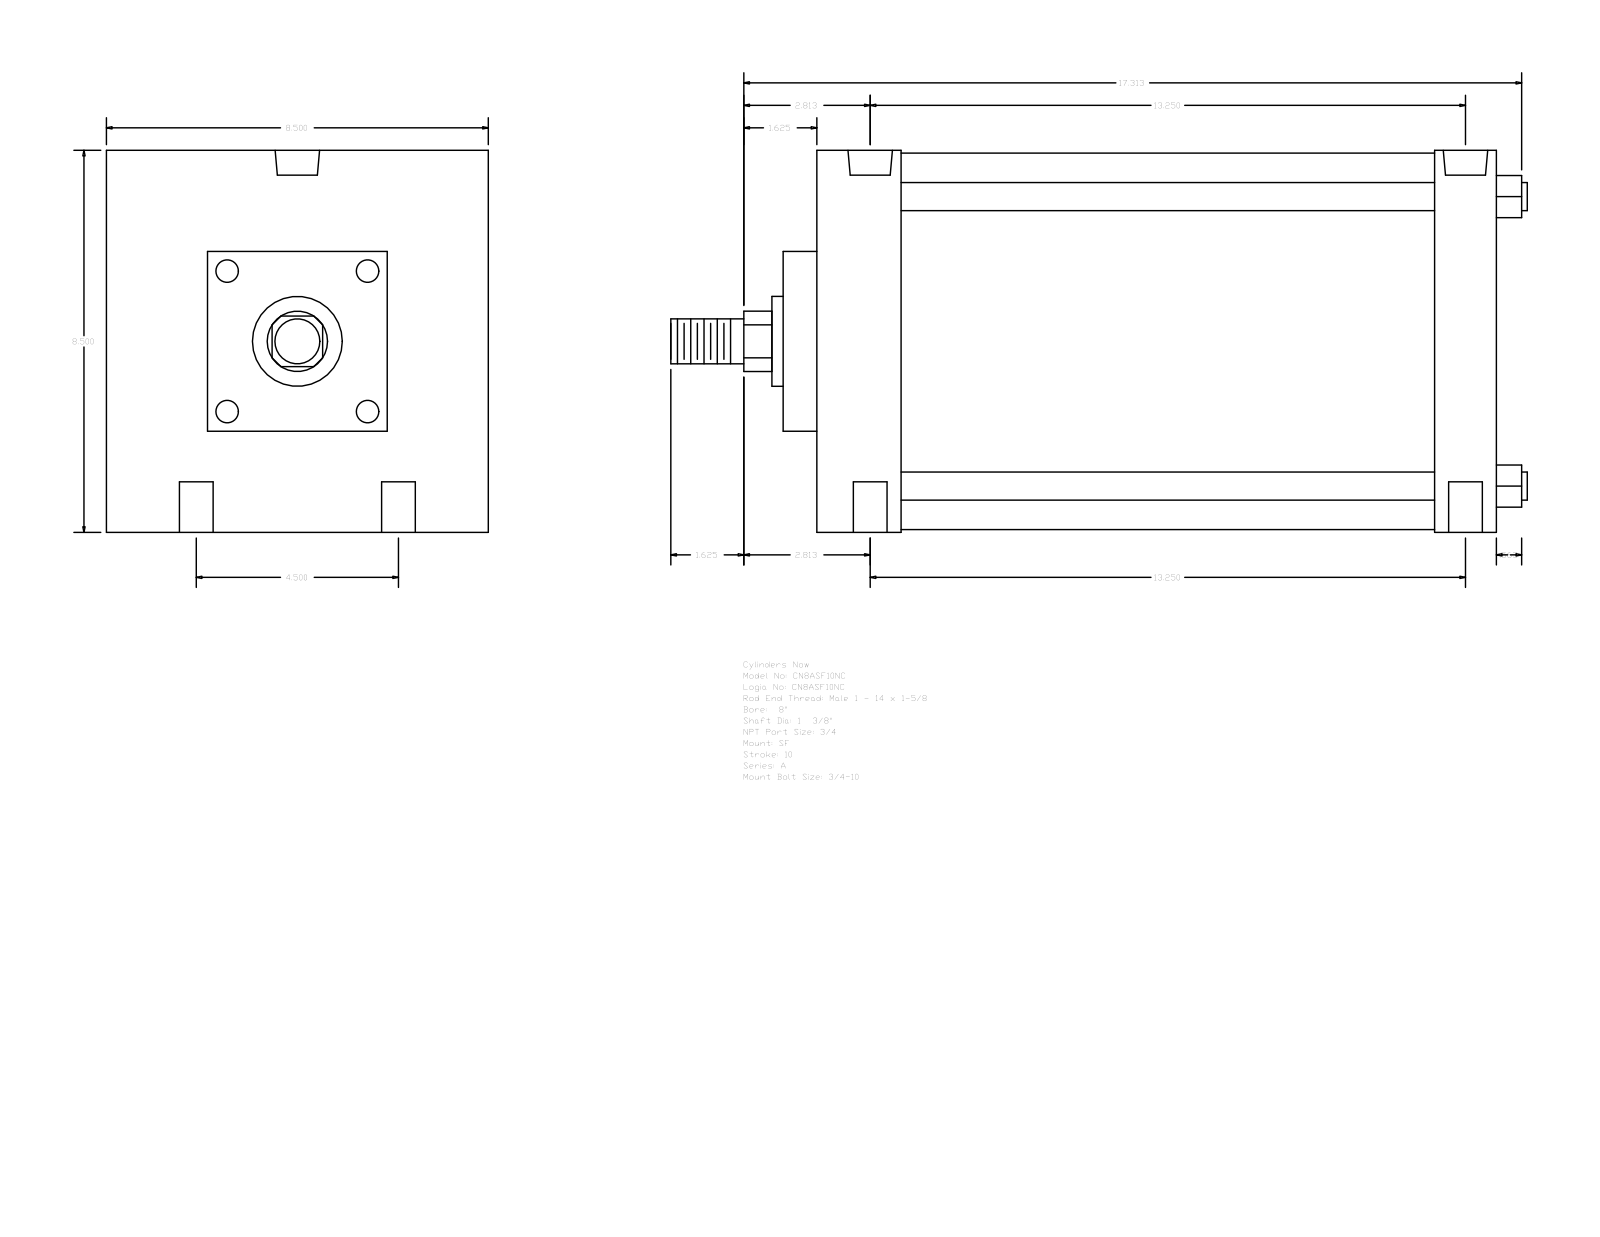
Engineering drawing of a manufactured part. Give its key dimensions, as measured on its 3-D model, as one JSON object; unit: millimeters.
{"part_name": "A_SF__0800_1.375", "step_written_by": "GSSL Pune (CONFIG_CONTROL_DESIGN)", "units": "millimeters", "bodies": {"solids": 0, "faces": 93, "planar": 67, "cylindrical": 26, "other": 0}, "overall_size": [484.19, 215.9, 215.9], "round_holes": [[19.05, 4], [15.08, 2], [25.12, 2]], "round_bosses_or_shafts": [[15.88, 4], [212.72, 1], [50.8, 1], [34.92, 1], [25.4, 1]], "partial_cylinders_radius": [[17.06, 1]], "face_to_face_distances": [384.18, 215.9, 47.63, 349.25, 301.62, 336.55, 34.93, 19.04, 66.67, 368.29], "hole_center_spacings": [57.15, 341.37, 336.55, 114.3, 355.43, 323.85]}
